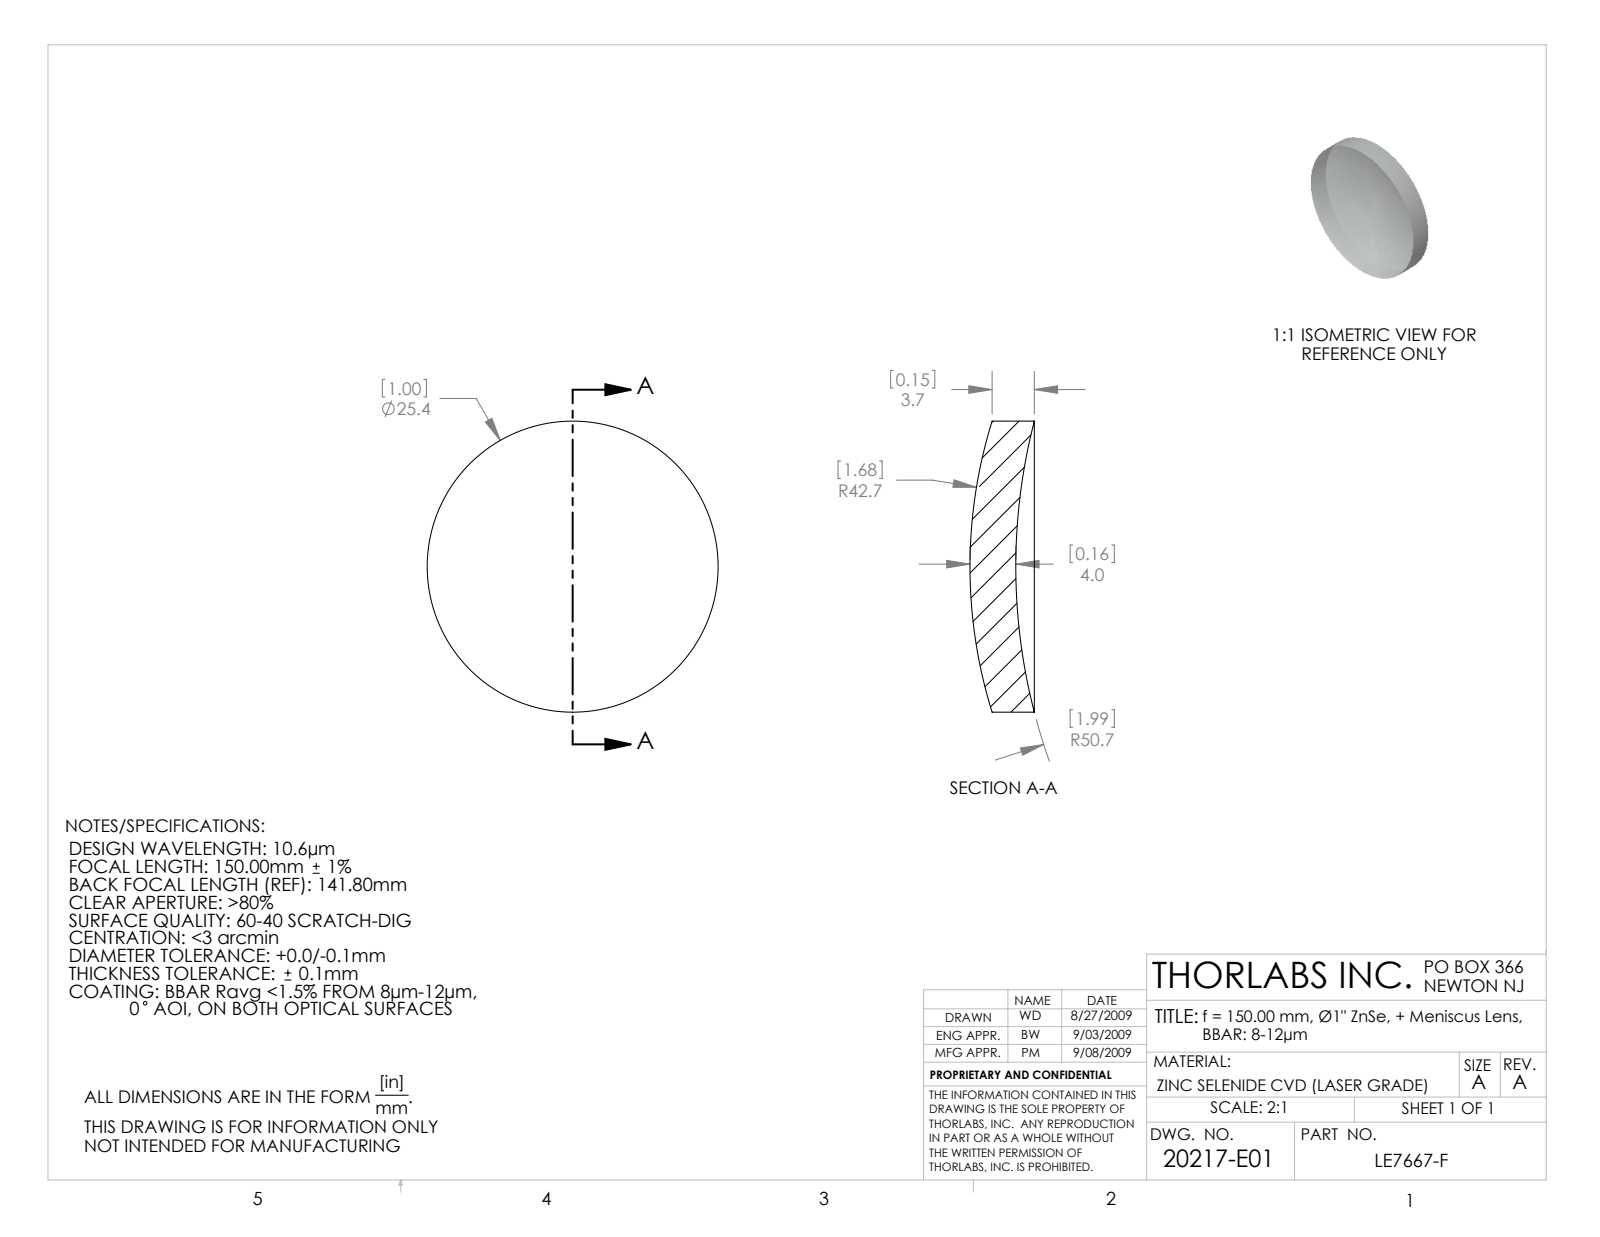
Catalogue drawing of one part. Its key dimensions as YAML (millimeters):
part_name: "20217-E0W"
step_written_by: "SolidWorks 2007 (CONFIG_CONTROL_DESIGN)"
units: millimeters
bodies: {solids: 1, faces: 6, planar: 0, cylindrical: 2, other: 4}
overall_size: [25.4, 25.4, 5.62]
volume: 1949
surface_area: 1327
round_bosses_or_shafts:
  - {diameter: 25.4, count: 1}
